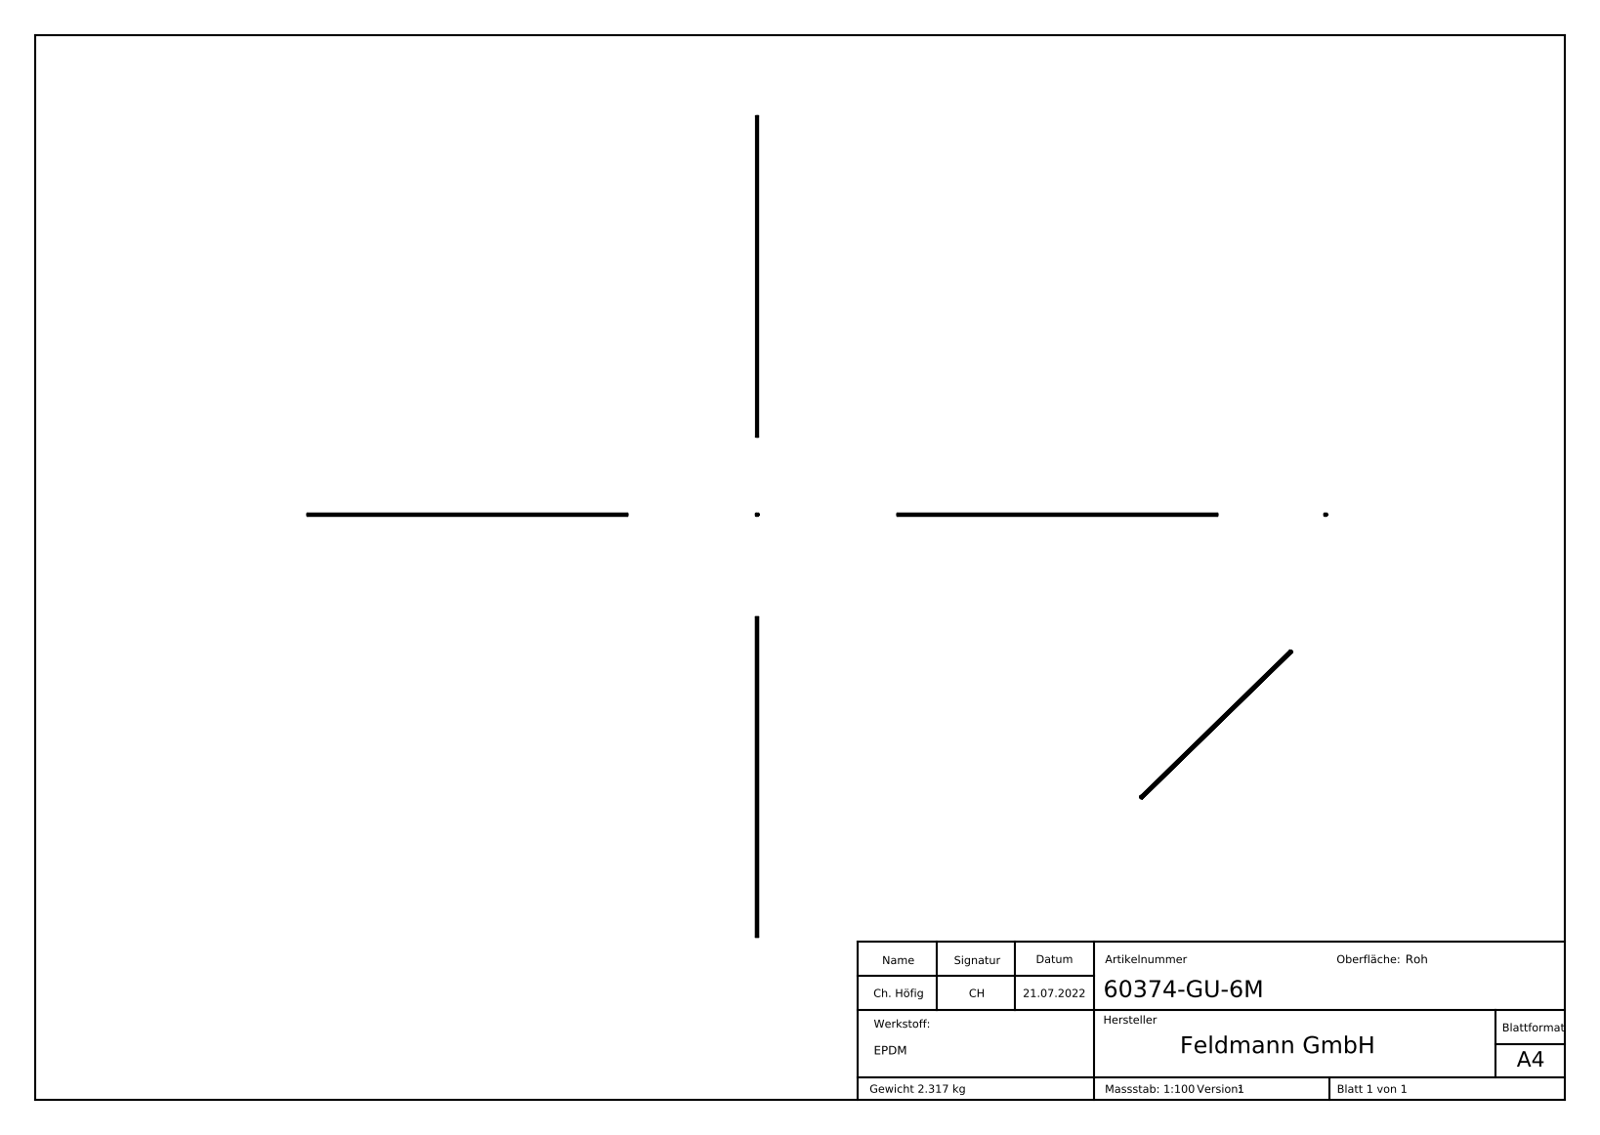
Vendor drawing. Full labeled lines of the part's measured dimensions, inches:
Part name (STEP PRODUCT): 60374-GU-6M
STEP written by: SolidWorks 2018 (CONFIG_CONTROL_DESIGN)
Units: inches
Bodies: 1 solid, 375 faces (222 planar, 28 cylindrical, 125 other)
Overall size (bounding box): 236.22 × 1.654 × 1.43
Volume: 119.7 in³ · Surface area: 2 525 in²
Partial cylindrical surfaces — rounded edges, fillets, slot ends (radius × count): R0.012 ×14, R0.063 ×4, R0.008 ×2, R0.02 ×2, R0.024 ×2, R0.602 ×2, R1.194 ×2
Main face-to-face distances: 0.118, 1.22, 0.24, 0.079, 1.339, 1.102, 0.047, 0.48, 0.287, 0.193
